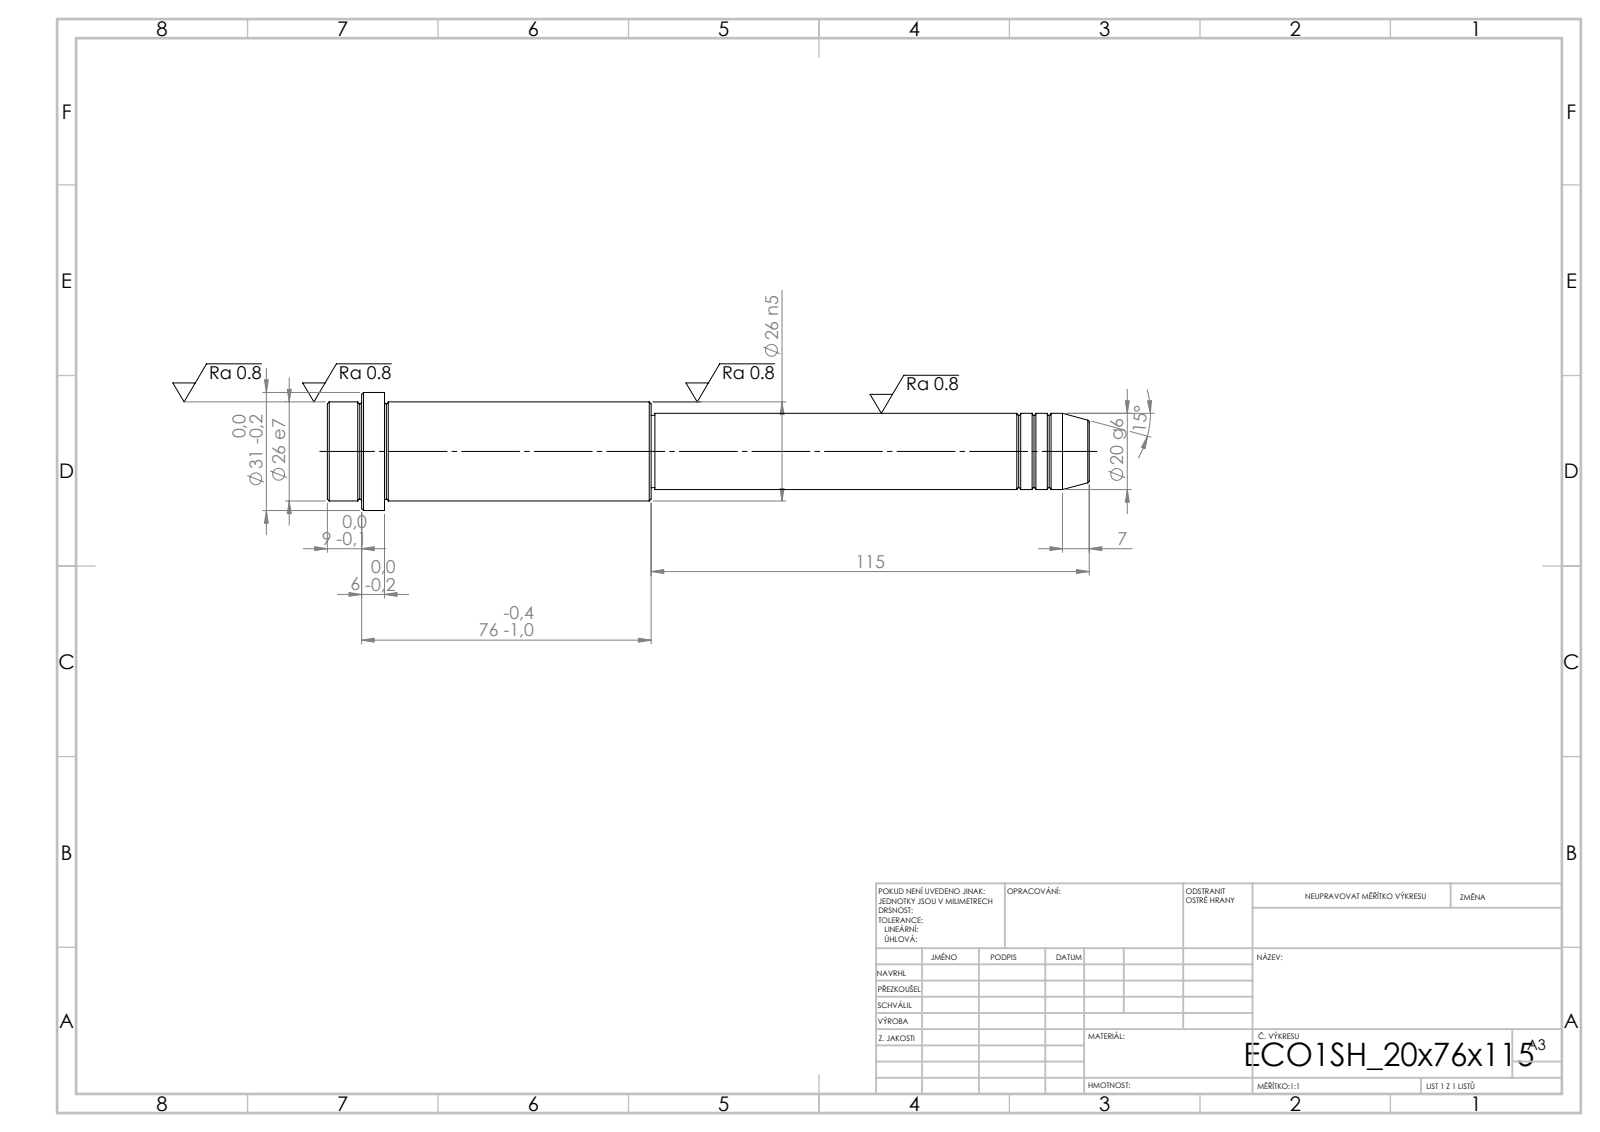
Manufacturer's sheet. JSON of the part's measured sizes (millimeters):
{"step_written_by": "SolidWorks 2019 (CONFIG_CONTROL_DESIGN)", "units": "millimeters", "bodies": {"solids": 1, "faces": 52, "planar": 6, "cylindrical": 16, "other": 30}, "overall_size": [200, 31, 31], "volume_mm3": 82014, "surface_area_mm2": 15798, "round_bosses_or_shafts": [[31, 1], [26, 1], [20, 1], [19, 1]], "face_to_face_distances": [15, 70, 85, 115, 185, 200, 191, 76, 6, 9]}
